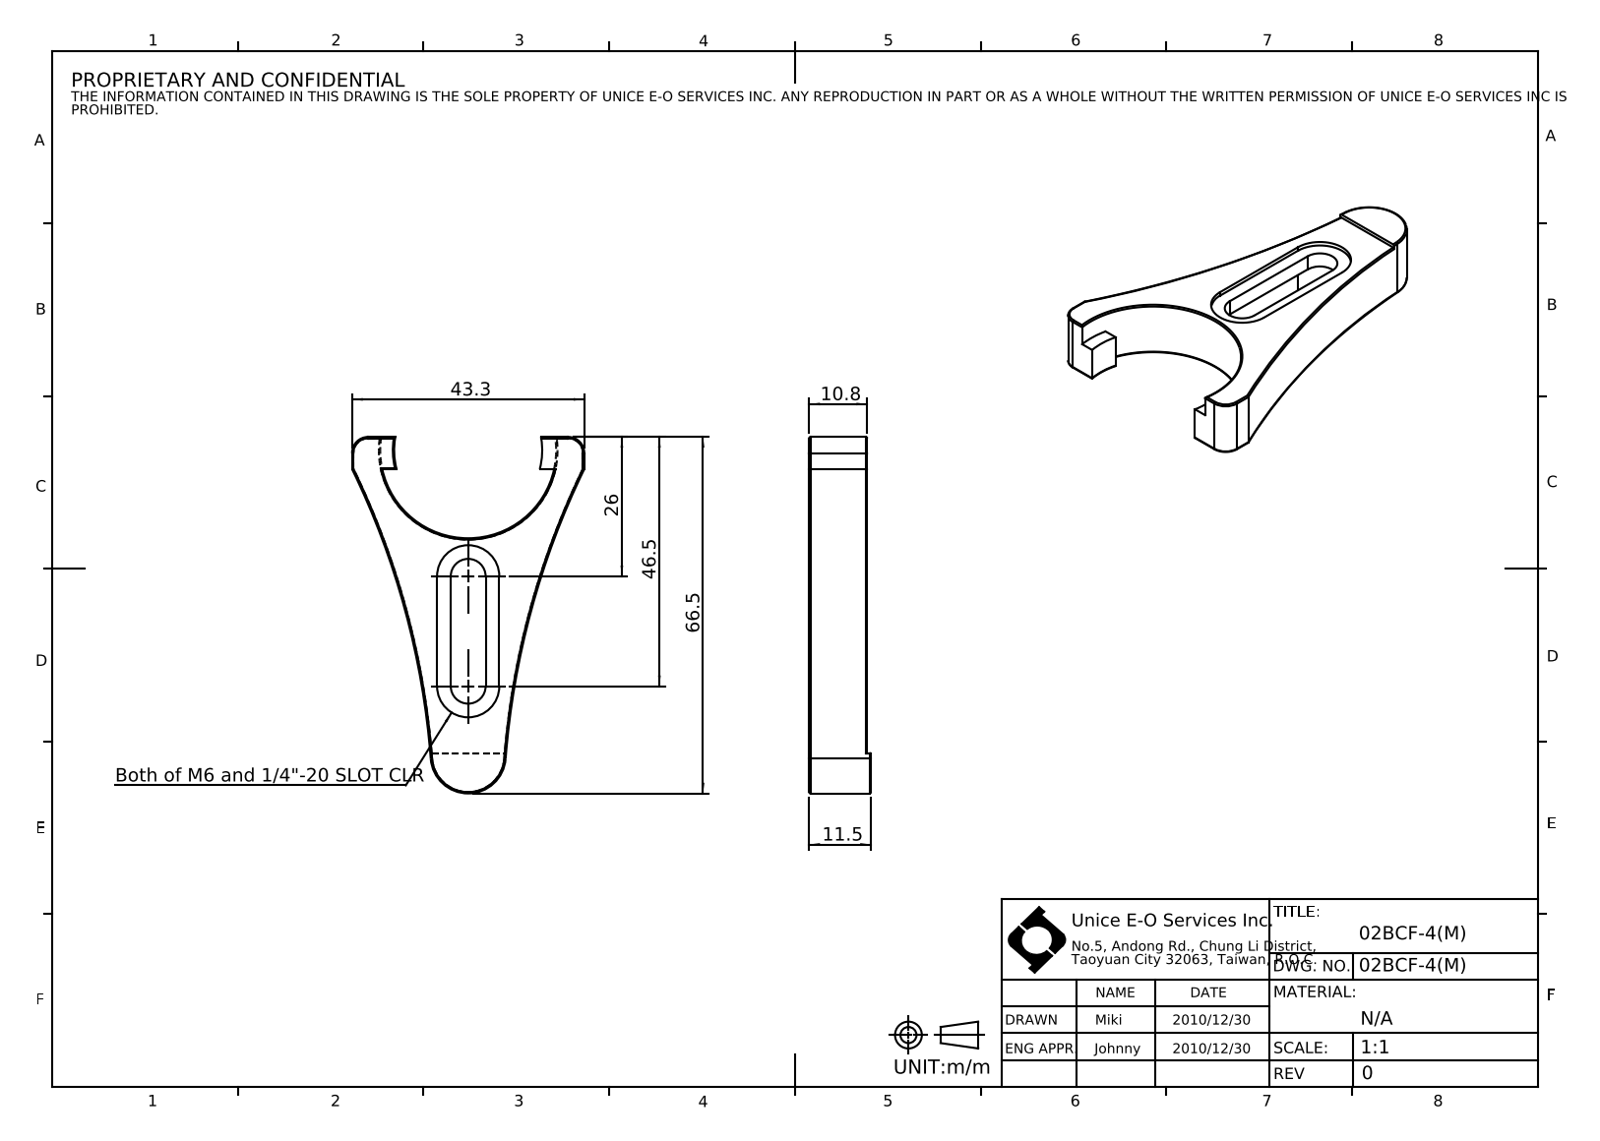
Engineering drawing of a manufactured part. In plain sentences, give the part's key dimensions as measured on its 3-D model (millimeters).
The part is named "02BCF-4(M)". Its 3-D file was written by "SolidWorks 2016 (CONFIG_CONTROL_DESIGN)". It is 1 solid with 63 faces: 20 planar, 26 cylindrical and 17 other. Overall it measures 66.5 by 43.3 by 11.5 millimeters. Its volume is 9 734 cubic millimeters and its surface area 5 185 square millimeters. Partial cylindrical surfaces (rounded edges, fillets, slot ends): 7 of radius 0.25, 2 of radius 3, 2 of radius 3.25, 2 of radius 5.8, 2 of radius 150, 1 of radius 7, 1 of radius 13.8, 1 of radius 16.4. The main face-to-face distances are 10.8, 0.8, 10, 3.8, 3, 7, 11.6, 2.55, 9.05, 0.7.
